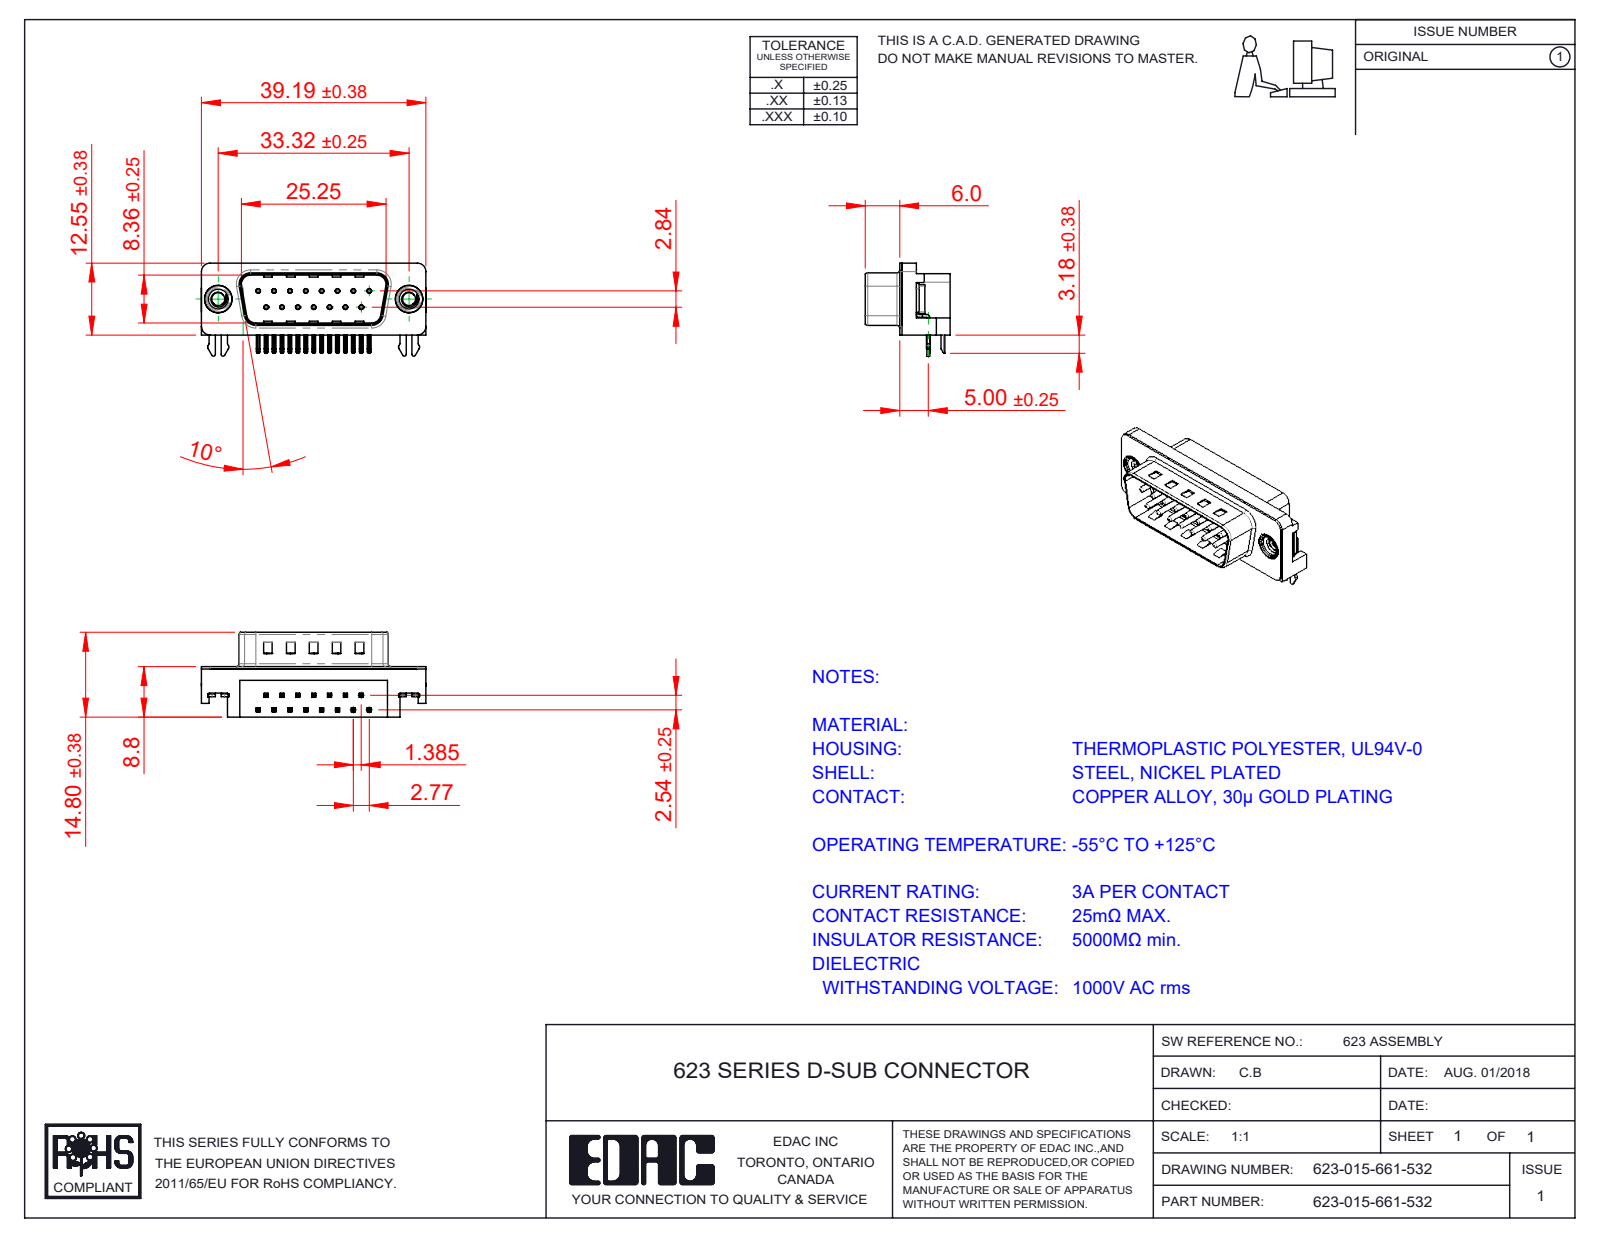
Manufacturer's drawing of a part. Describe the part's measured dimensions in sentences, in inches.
The part is named "623 4-40 Threaded Rivet; 623 Housing_15 Socket; 623 2 Prong Board Lock; 623 Contact Top (+3 more)". Its 3-D file was written by "SolidWorks 2016 (CONFIG_CONTROL_DESIGN)". It is 21 solids with 1499 faces: 921 planar, 439 cylindrical and 139 other. Overall it measures 1.544 by 0.64 by 0.583 inches. Its volume is 0.203 cubic inches and its surface area 7.668 square inches. Round holes: 15 of diameter 0.014, 15 of diameter 0.031, 2 of diameter 0.089, 2 of diameter 0.157, 2 of diameter 0.189, 2 of diameter 0.197. Round bosses or shafts: 15 of diameter 0.03, 2 of diameter 0.193, 2 of diameter 0.187, 2 of diameter 0.154. Partial cylindrical surfaces (rounded edges, fillets, slot ends): 68 of radius 0.01, 30 of radius 0.005, 14 of radius 0.02, 8 of radius 0.039, 6 of radius 0.059, 4 of radius 0.013, 4 of radius 0.035, 4 of radius 0.063. The main face-to-face distances are 0.016, 0.331, 0.083, 0.067, 0.412, 0.346, 0.428, 0.345, 0.232, 0.114. The hole center spacings are 0.124, 0.109, 0.218, 0.327, 0.436, 0.198, 0.198, 0.294.
